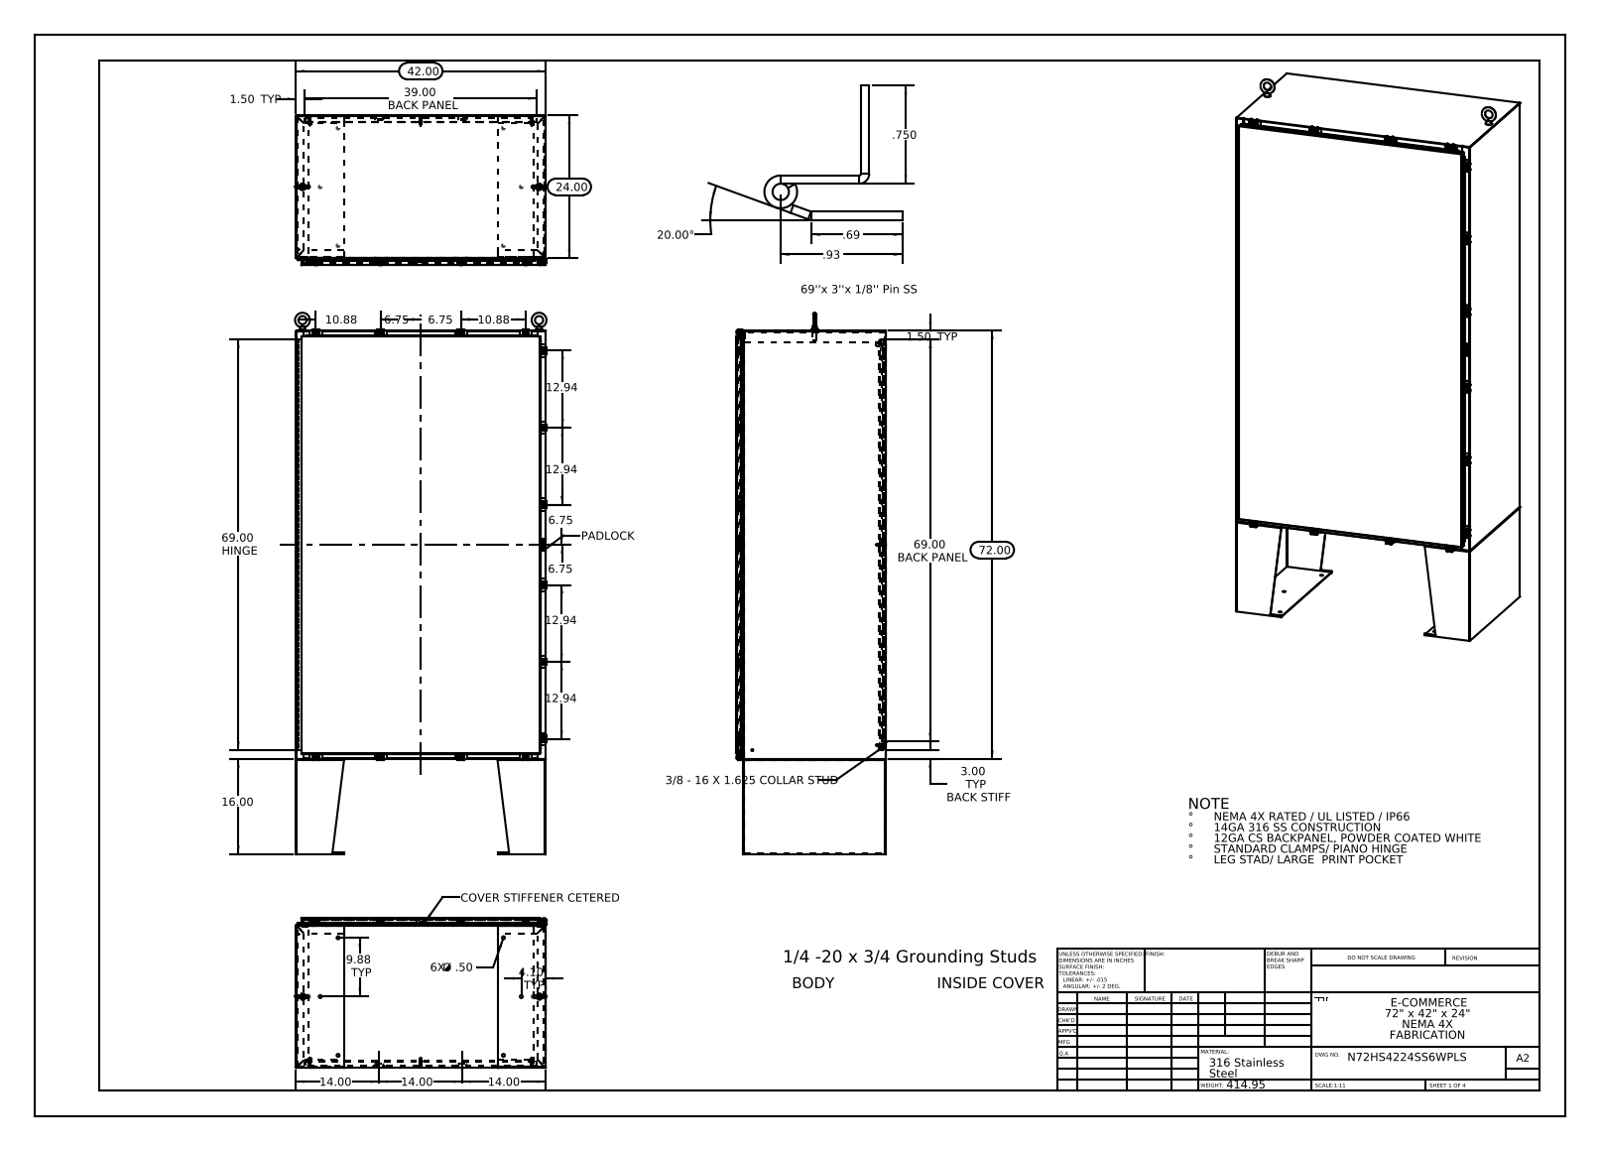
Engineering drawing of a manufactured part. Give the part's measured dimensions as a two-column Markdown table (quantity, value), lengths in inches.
| quantity | value |
| --- | --- |
| part name | N72HS4224SSWPLS Padlock Staple; N72HS4224SSWPLS SD-LSK - Base; Eye-Bolt_Stiffener WMT Template 1907; 10_30 CD Stud (+8 more) |
| STEP written by | SolidWorks 2013 (CONFIG_CONTROL_DESIGN) |
| units | inches |
| bodies | 108 solids, 4313 faces (2196 planar, 1809 cylindrical, 308 other) |
| overall size | 91 × 42.346 × 25.201 |
| volume | 1 468 in³ |
| surface area | 35 616 in² |
| round holes (diameter × count) | 0.213 × 14, 0.26 × 14, 0.5 × 14, 0.25 × 8, 0.75 × 4, 0.125 × 2, 0.125 × 1 |
| round bosses / shafts (diameter × count) | 0.25 × 15, 0.5 × 14, 0.399 × 14, 0.625 × 10, 0.375 × 8, 0.33 × 8, 0.157 × 8, 0.14 × 8 |
| partial cylindrical surfaces (radius × count) | 0.06 × 62, 0.013 × 39, 0.088 × 33, 0.12 × 28, 0.141 × 28, 0.05 × 25, 0.145 × 24, 0.08 × 20 |
| main face-to-face distances | 0.075, 25.126, 0.104, 41.925, 25.051, 1.075, 25.201, 24.126, 1, 24.051 |
| hole center spacings | 7.069, 2.225, 10.324, 11.553, 33.625, 35.196, 35.74, 38.439 |
